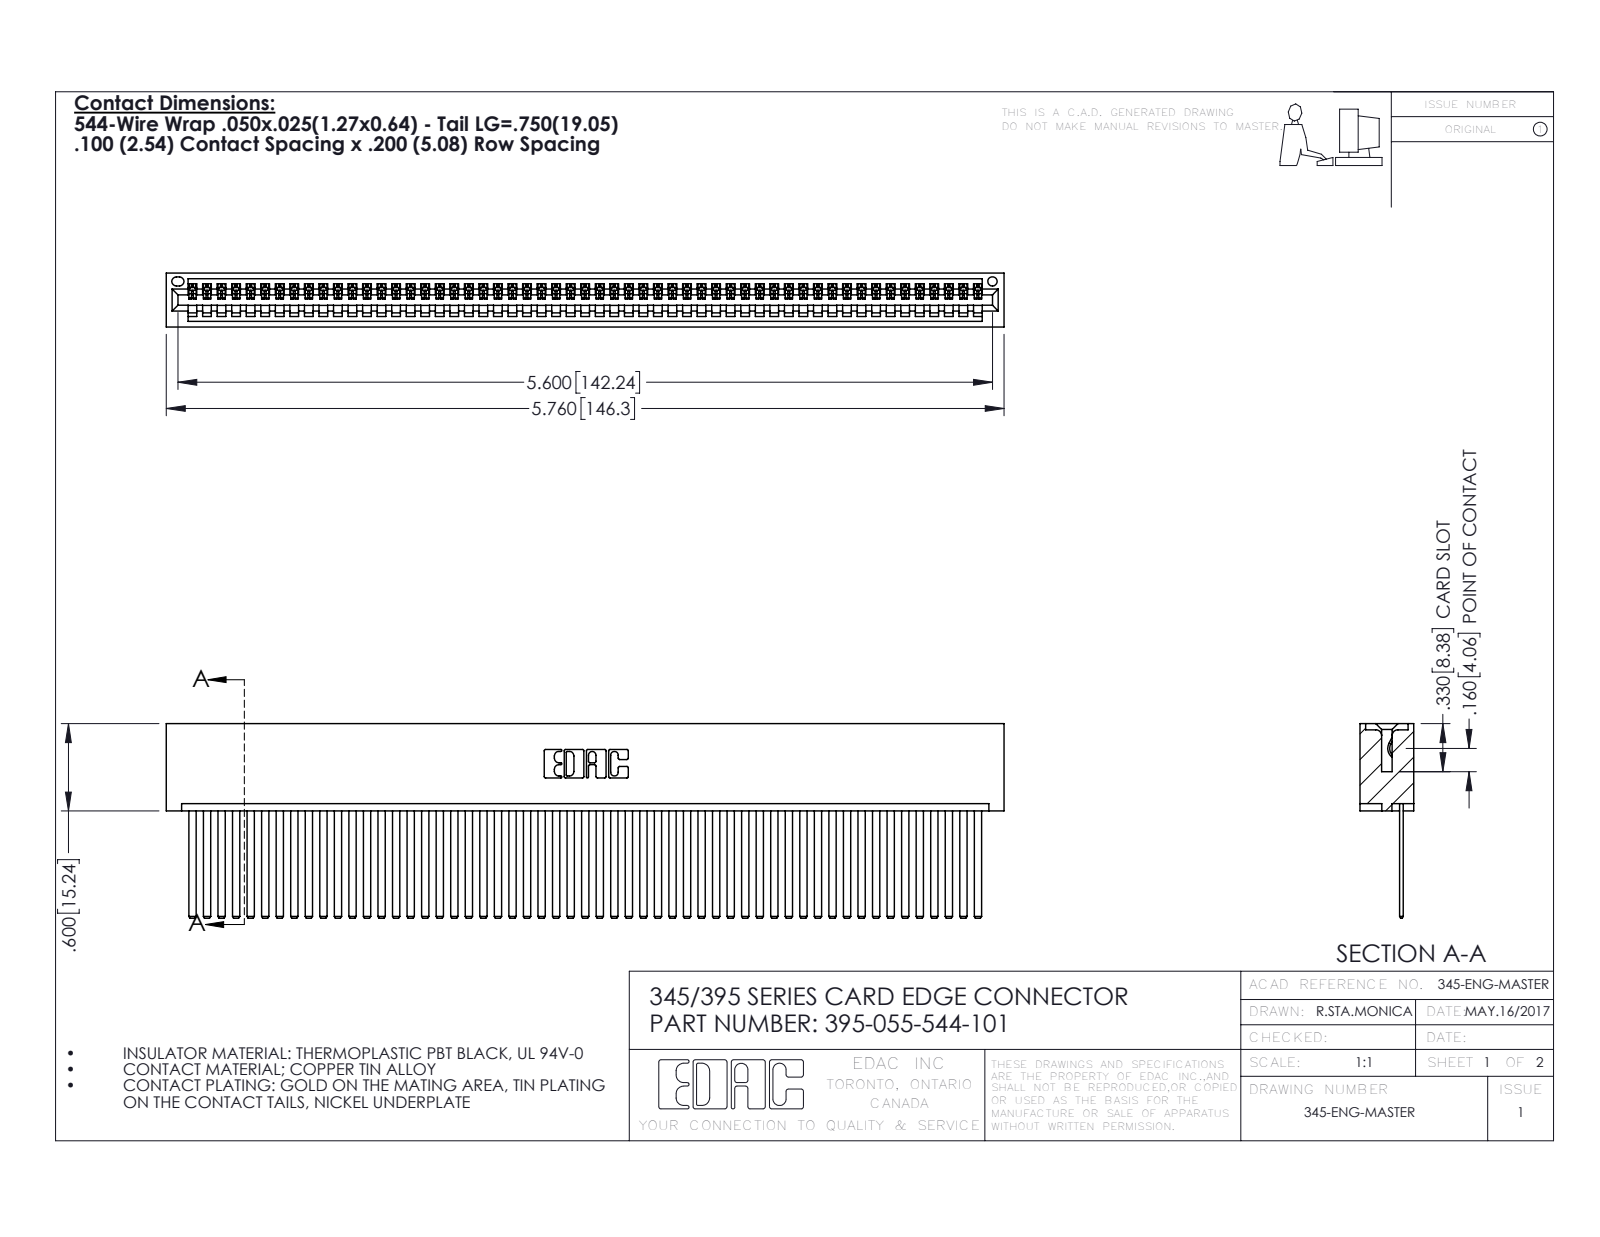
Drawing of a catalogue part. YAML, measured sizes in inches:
part_name: "345-292-001_345-293-144; 345 Part_No Mounting Lugs; 395-055-544-101"
step_written_by: "SolidWorks 2016 (CONFIG_CONTROL_DESIGN)"
units: inches
bodies: {solids: 56, faces: 2978, planar: 2056, cylindrical: 922, other: 0}
overall_size: [5.76, 1.337, 0.37]
volume: 0.929
surface_area: 34.89
round_holes:
  - {diameter: 0.064, count: 1}
partial_cylinders:
  - {radius: 0.006, count: 110}
  - {radius: 0.01, count: 22}
  - {radius: 0.007, count: 6}
  - {radius: 0.031, count: 6}
  - {radius: 0.026, count: 3}
  - {radius: 0.031, count: 2}
  - {radius: 0.04, count: 2}
  - {radius: 0.014, count: 1}
face_to_face_distances: [0.072, 0.298, 0.025, 0.098, 0.272, 0.37, 0.2, 0.225, 0.149, 0.072]
